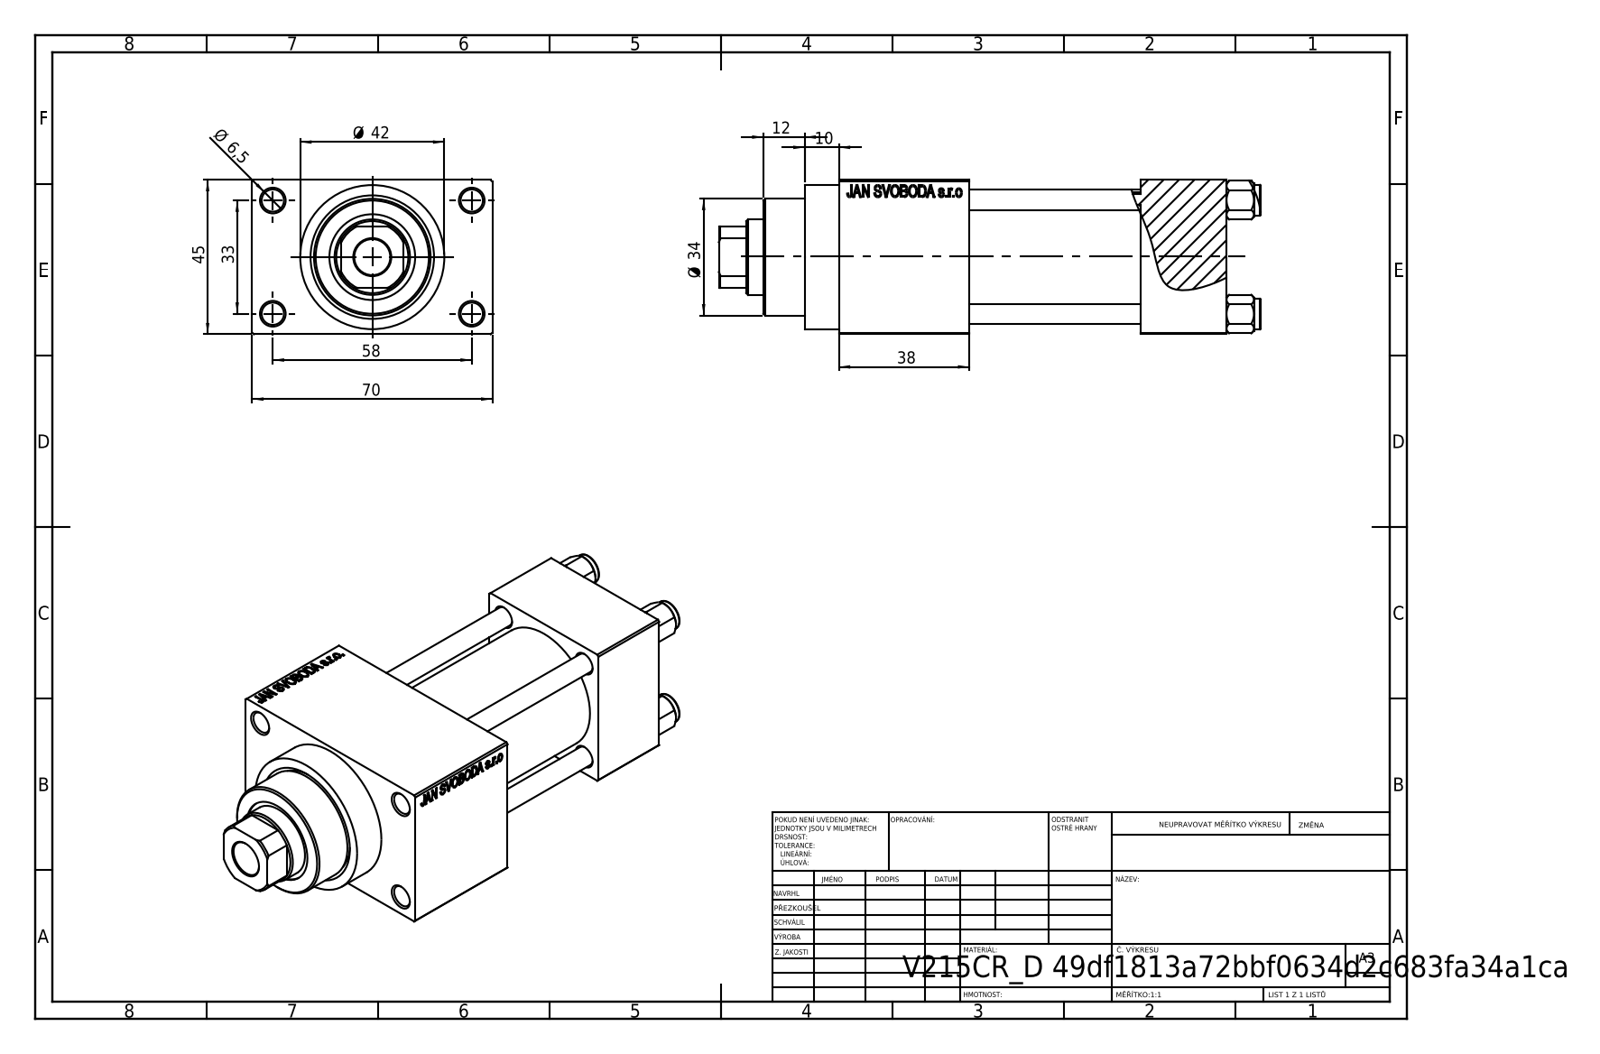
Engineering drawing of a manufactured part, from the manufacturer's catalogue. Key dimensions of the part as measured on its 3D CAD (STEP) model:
Part name (STEP PRODUCT): V215CR_VCP_D; V215CR_D_TYCINKA; V215CR_D_Body; NUT_M5_D (+1 more)
STEP written by: SolidWorks 2019 (CONFIG_CONTROL_DESIGN)
Units: millimetres
Bodies: 11 solids, 1104 faces (496 planar, 88 cylindrical, 520 other)
Overall size (bounding box): 158 × 70 × 45
Volume: 242 876 mm³ · Surface area: 79 884 mm²
Round holes (diameter × count): ⌀6 ×4, ⌀6.5 ×4, ⌀7 ×2, ⌀13.16 ×2, ⌀20 ×2, ⌀10.5 ×1, ⌀22 ×1, ⌀24 ×1, ⌀25 ×1, ⌀32 ×1, ⌀33 ×1
Round bosses / shafts (diameter × count): ⌀9 ×4, ⌀42 ×1, ⌀38 ×1, ⌀34 ×1
Partial cylindrical surfaces — rounded edges, fillets, slot ends (radius × count): R10.5 ×1
Main face-to-face distances: 45, 25, 50, 12.5, 75, 57.5, 88, 38, 113, 70
Hole centre spacings: 12.4, 23.48, 33.2, 33.37, 35.35, 45.6, 56.35, 33
